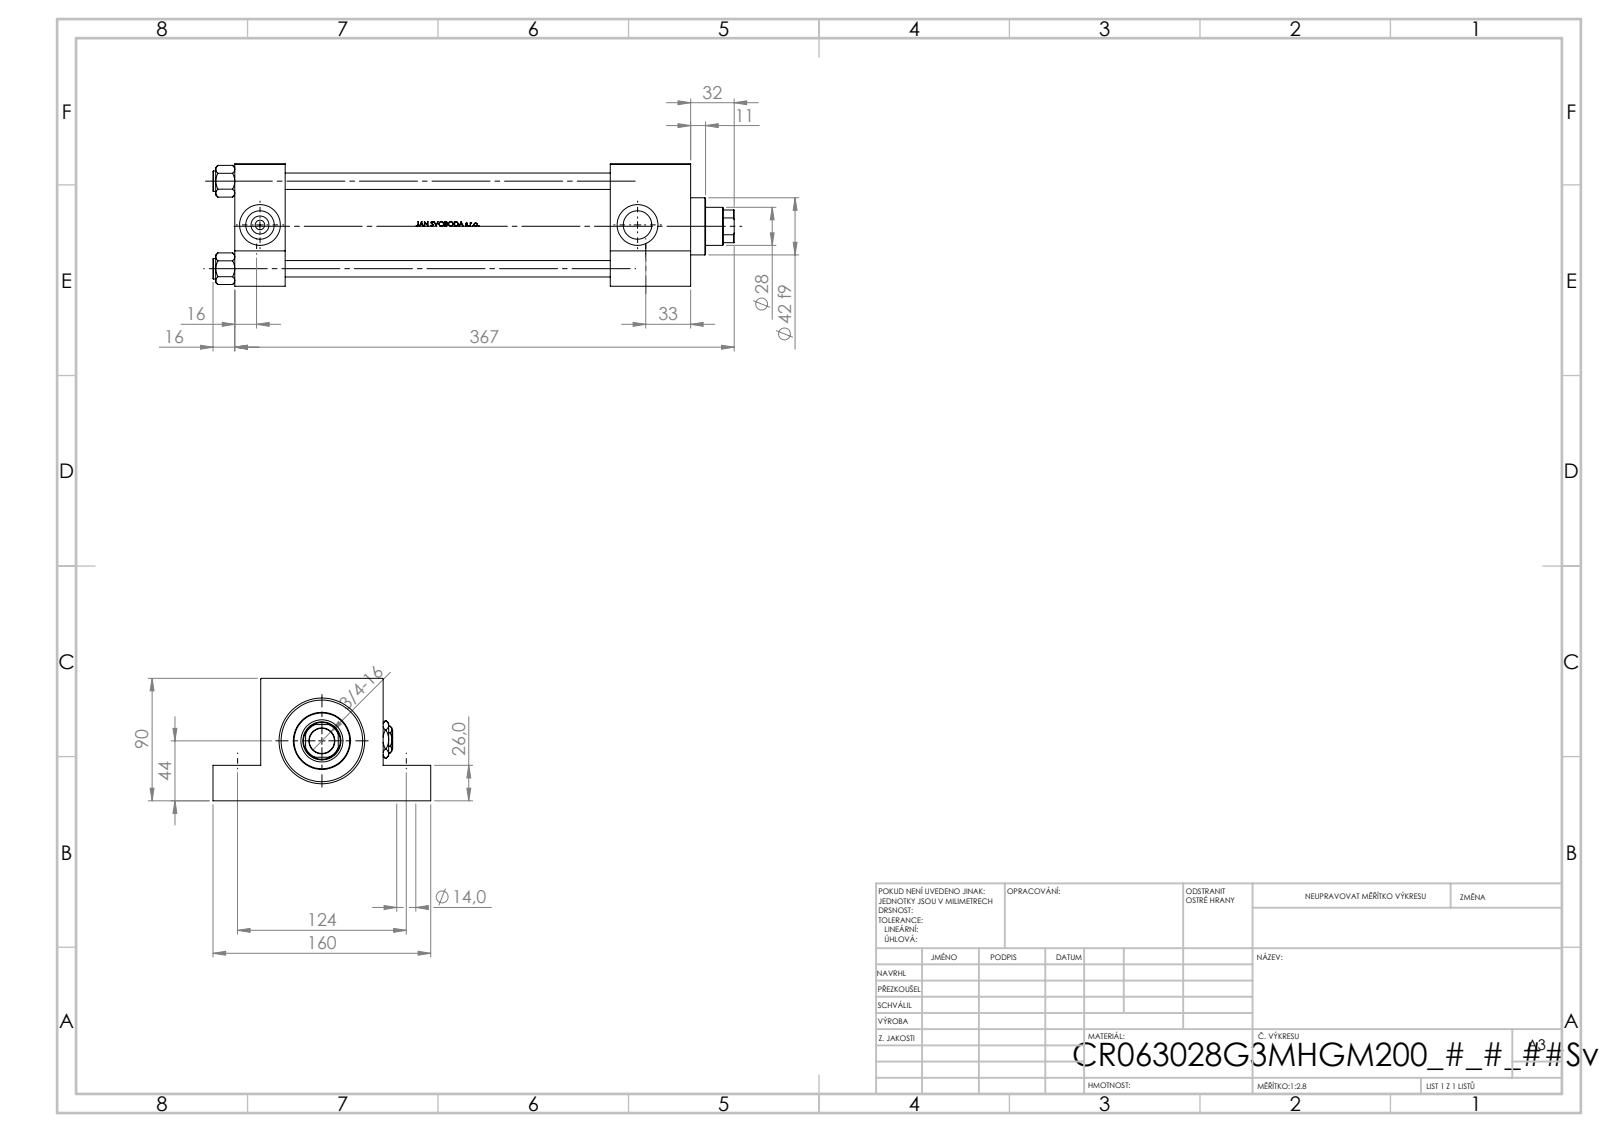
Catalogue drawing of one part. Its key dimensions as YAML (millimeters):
part_name: "Zatka_pro_OIL_PORT; V215CR_G_TYCINKA; NUT_M5_G; V215CR_VCP_G (+2 more)"
step_written_by: "SolidWorks 2019 (CONFIG_CONTROL_DESIGN)"
units: millimeters
bodies: {solids: 13, faces: 1184, planar: 478, cylindrical: 132, other: 574}
overall_size: [383, 160, 90]
volume: 1414000
surface_area: 321947
round_holes:
  - {diameter: 12, count: 4}
  - {diameter: 14, count: 4}
  - {diameter: 7, count: 2}
  - {diameter: 20.96, count: 2}
  - {diameter: 30, count: 2}
  - {diameter: 18.5, count: 1}
  - {diameter: 28, count: 1}
  - {diameter: 31, count: 1}
  - {diameter: 50, count: 1}
  - {diameter: 60, count: 1}
  - {diameter: 63, count: 1}
round_bosses_or_shafts:
  - {diameter: 15, count: 4}
  - {diameter: 69, count: 1}
  - {diameter: 42, count: 1}
partial_cylinders:
  - {radius: 13.5, count: 1}
face_to_face_distances: [90, 37, 298, 335, 59, 276, 239, 64, 26, 35]
hole_center_spacings: [64.3, 44.77, 46.18, 90.93, 124, 286, 311.72, 277.5]
